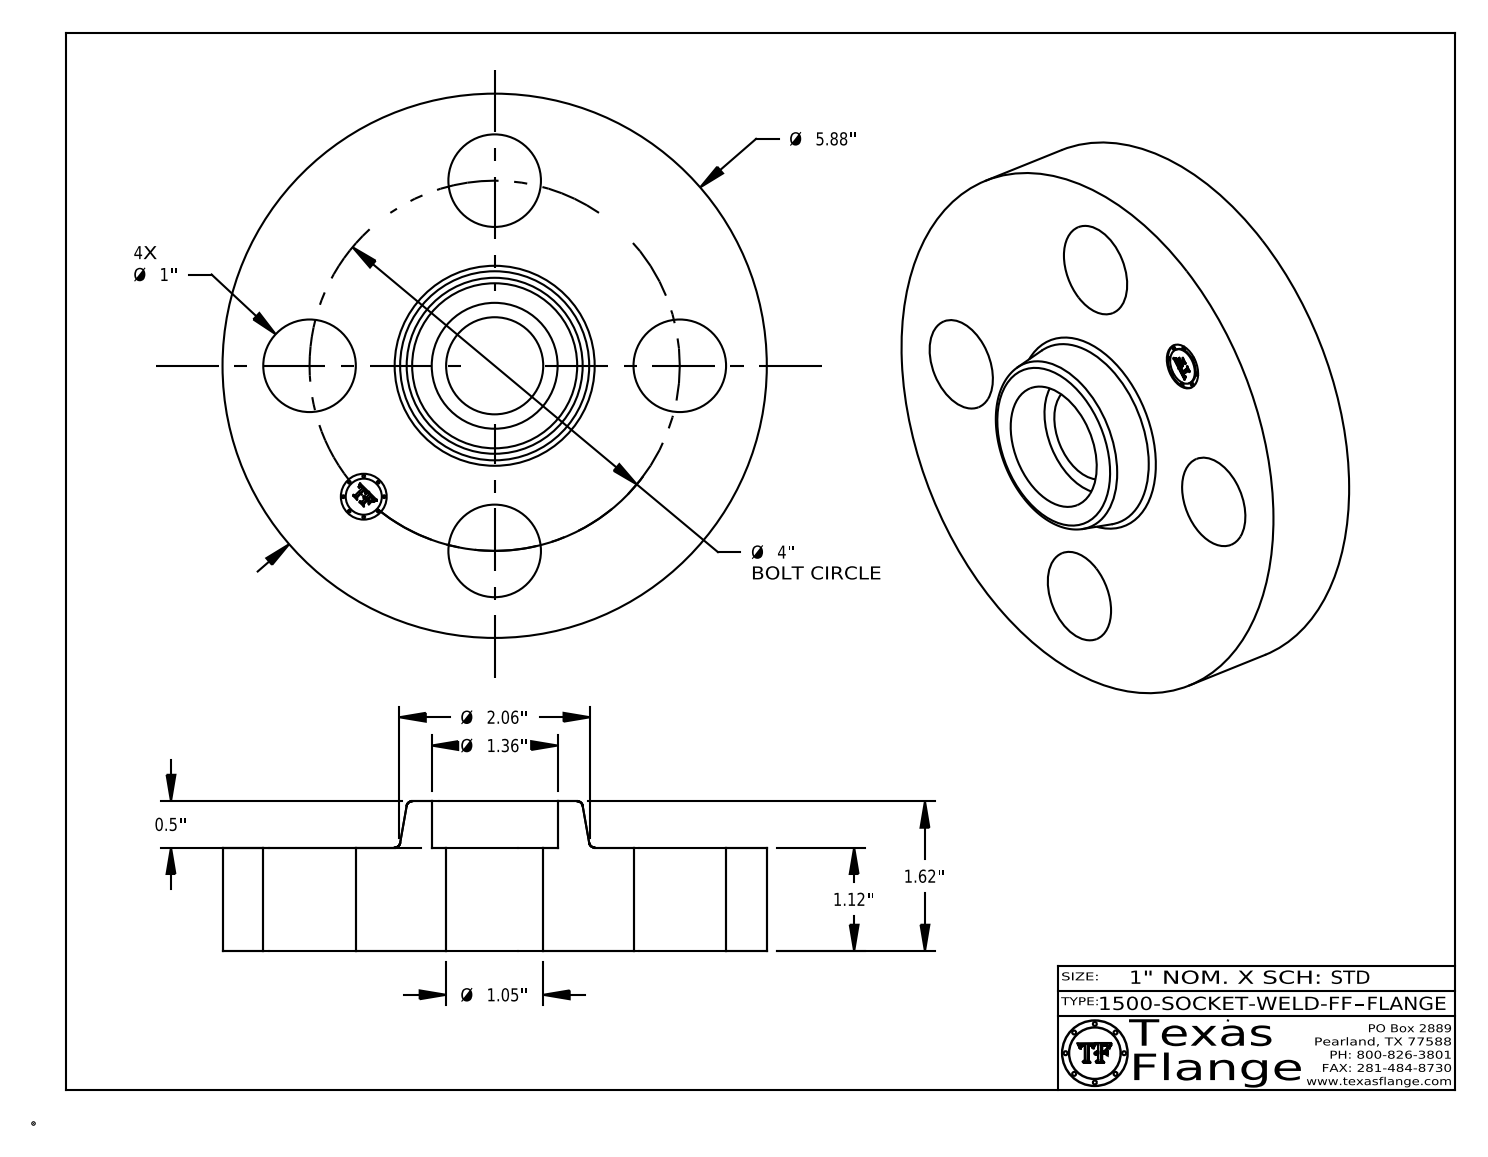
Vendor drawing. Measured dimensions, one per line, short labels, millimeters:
name: 1500-SOCKET-WELD-FF
written by: CATIA V5 STEP AP214 (AUTOMOTIVE_DESIGN)
unit: mm
bodies: 1 solid, 409 faces (369 planar, 34 cylindrical, 6 other)
size: 149.4 × 149.4 × 41.1
volume: 438 000 mm³; area: 57 660 mm²
holes: 4× ⌀25.4, 1× ⌀12.6, 1× ⌀26.6, 1× ⌀34.5
bosses: 8× ⌀0.8, 1× ⌀149.4, 1× ⌀9.9
face distances: 28.4, 41.1, 12.7, 0.4, 28.1, 13.1, 3.8, 3.7, 0.7, 2.4
hole spacings: 50.8, 71.8, 38.9, 93.9, 101.6
